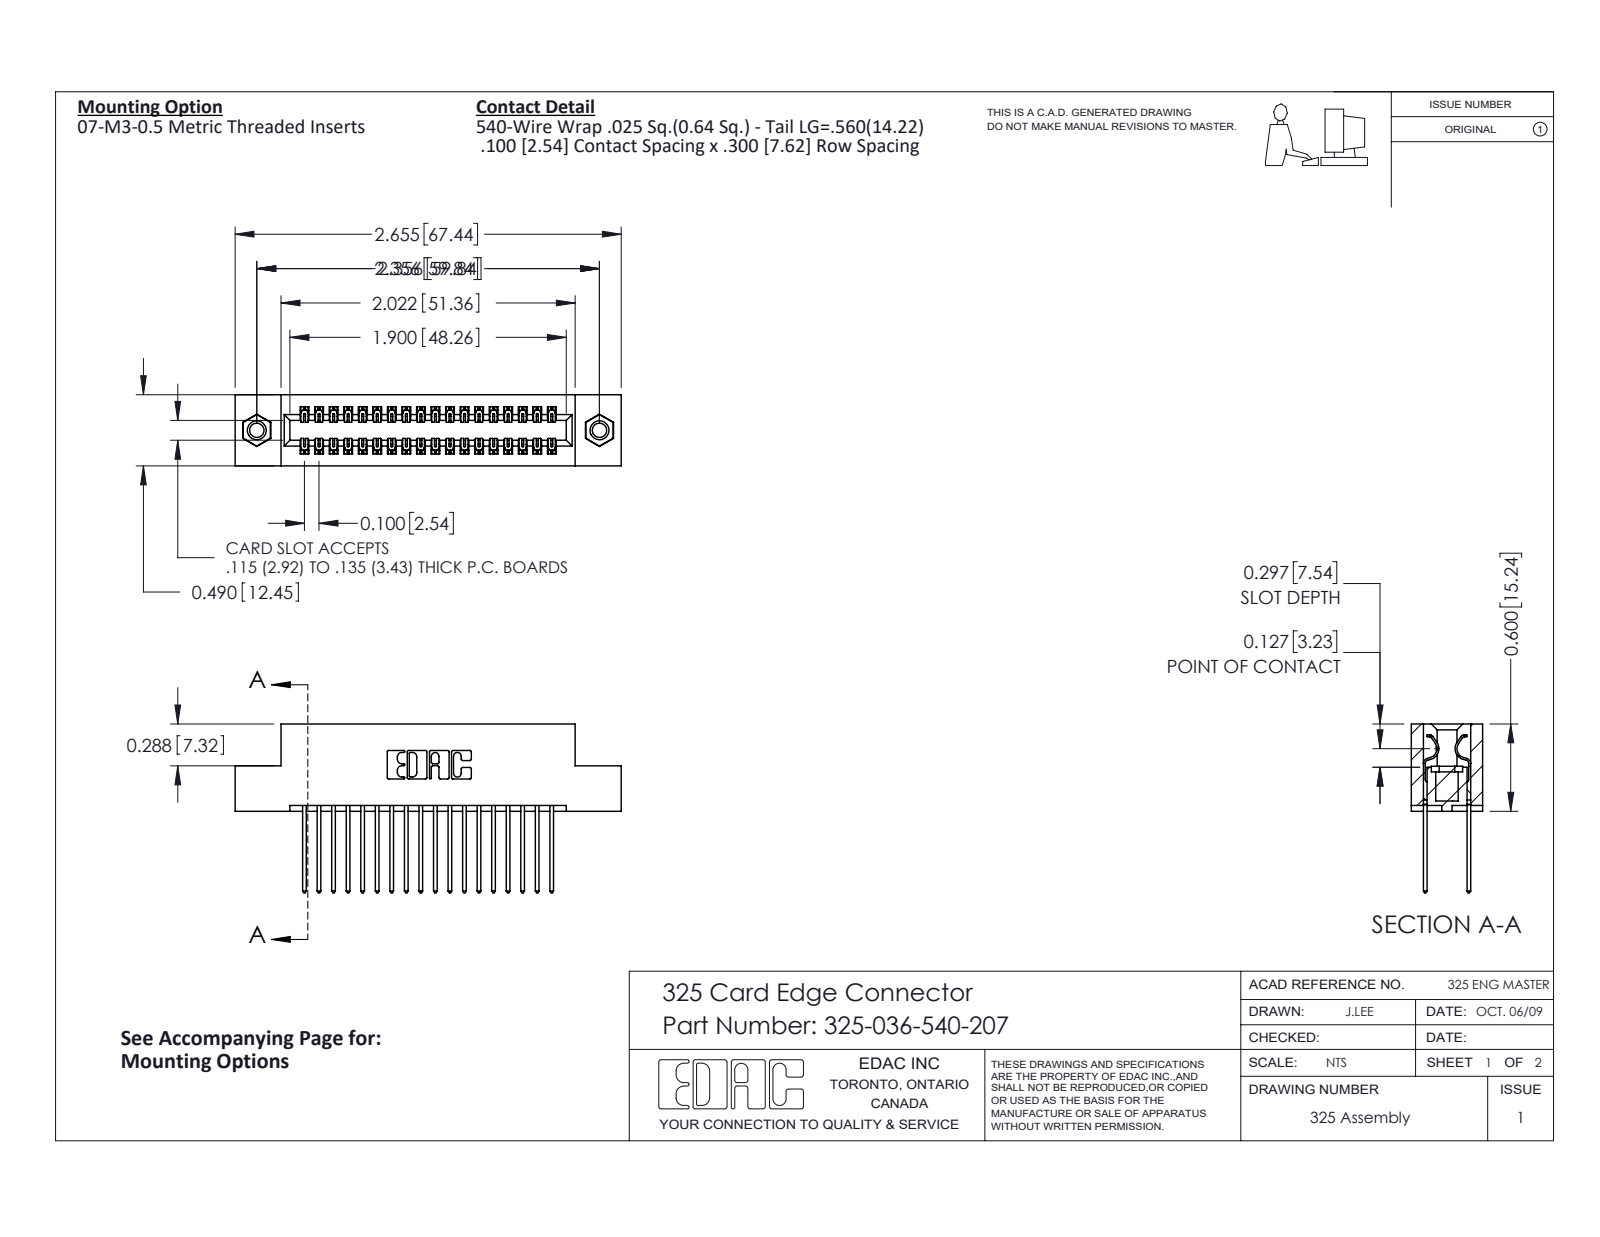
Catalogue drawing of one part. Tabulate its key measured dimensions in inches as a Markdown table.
| quantity | value |
| --- | --- |
| part name | 345-250-001_345-250-005-103; 325-292-001_325-293-140; 325 Part_TI; 325-036-540-207 |
| STEP written by | SolidWorks 2016 (CONFIG_CONTROL_DESIGN) |
| units | inches |
| bodies | 39 solids, 2046 faces (1398 planar, 632 cylindrical, 16 other) |
| overall size | 2.655 × 1.16 × 0.49 |
| volume | 0.526 in³ |
| surface area | 16.33 in² |
| round holes (diameter × count) | 0.098 × 2, 0.125 × 2, 0.16 × 2 |
| round bosses / shafts (diameter × count) | 0.155 × 2 |
| partial cylindrical surfaces (radius × count) | 0.006 × 54, 0.01 × 36, 0.01 × 22, 0.007 × 6, 0.031 × 6, 0.026 × 3, 0.014 × 2, 0.022 × 2 |
| main face-to-face distances | 0.083, 0.407, 0.3, 0.107, 0.383, 0.025, 0.49, 0.325, 0.6, 0.2 |
| hole center spacings | 2.356 |
